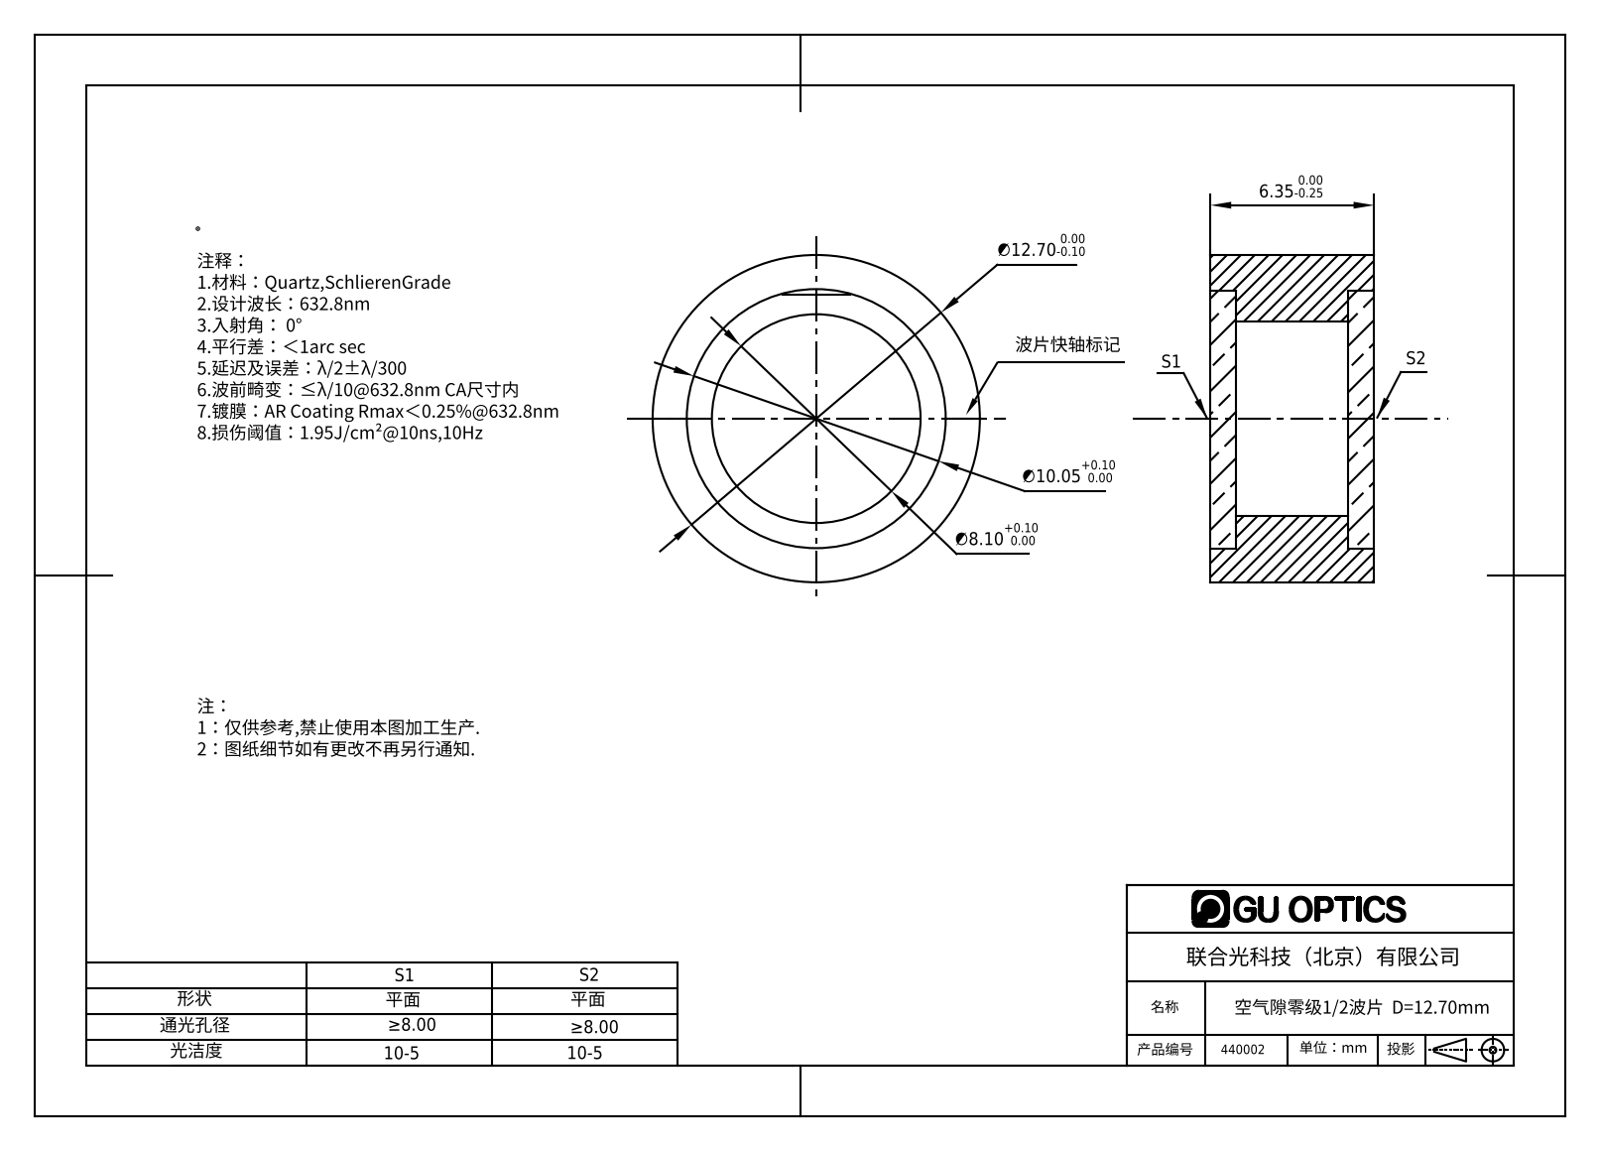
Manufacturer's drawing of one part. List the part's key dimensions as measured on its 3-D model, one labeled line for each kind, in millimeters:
Part name (STEP PRODUCT): 440002
STEP written by: SolidWorks 2016 (CONFIG_CONTROL_DESIGN)
Units: millimetres
Bodies: 3 solids, 20 faces (8 planar, 12 cylindrical, 0 other)
Overall size (bounding box): 12.7 × 12.7 × 6.35
Volume: 580 mm³ · Surface area: 958 mm²
Round holes (diameter × count): ⌀8.1 ×1, ⌀10.05 ×1
Round bosses / shafts (diameter × count): ⌀12.7 ×1
Main face-to-face distances: 1, 5.35, 6.35, 4.35
